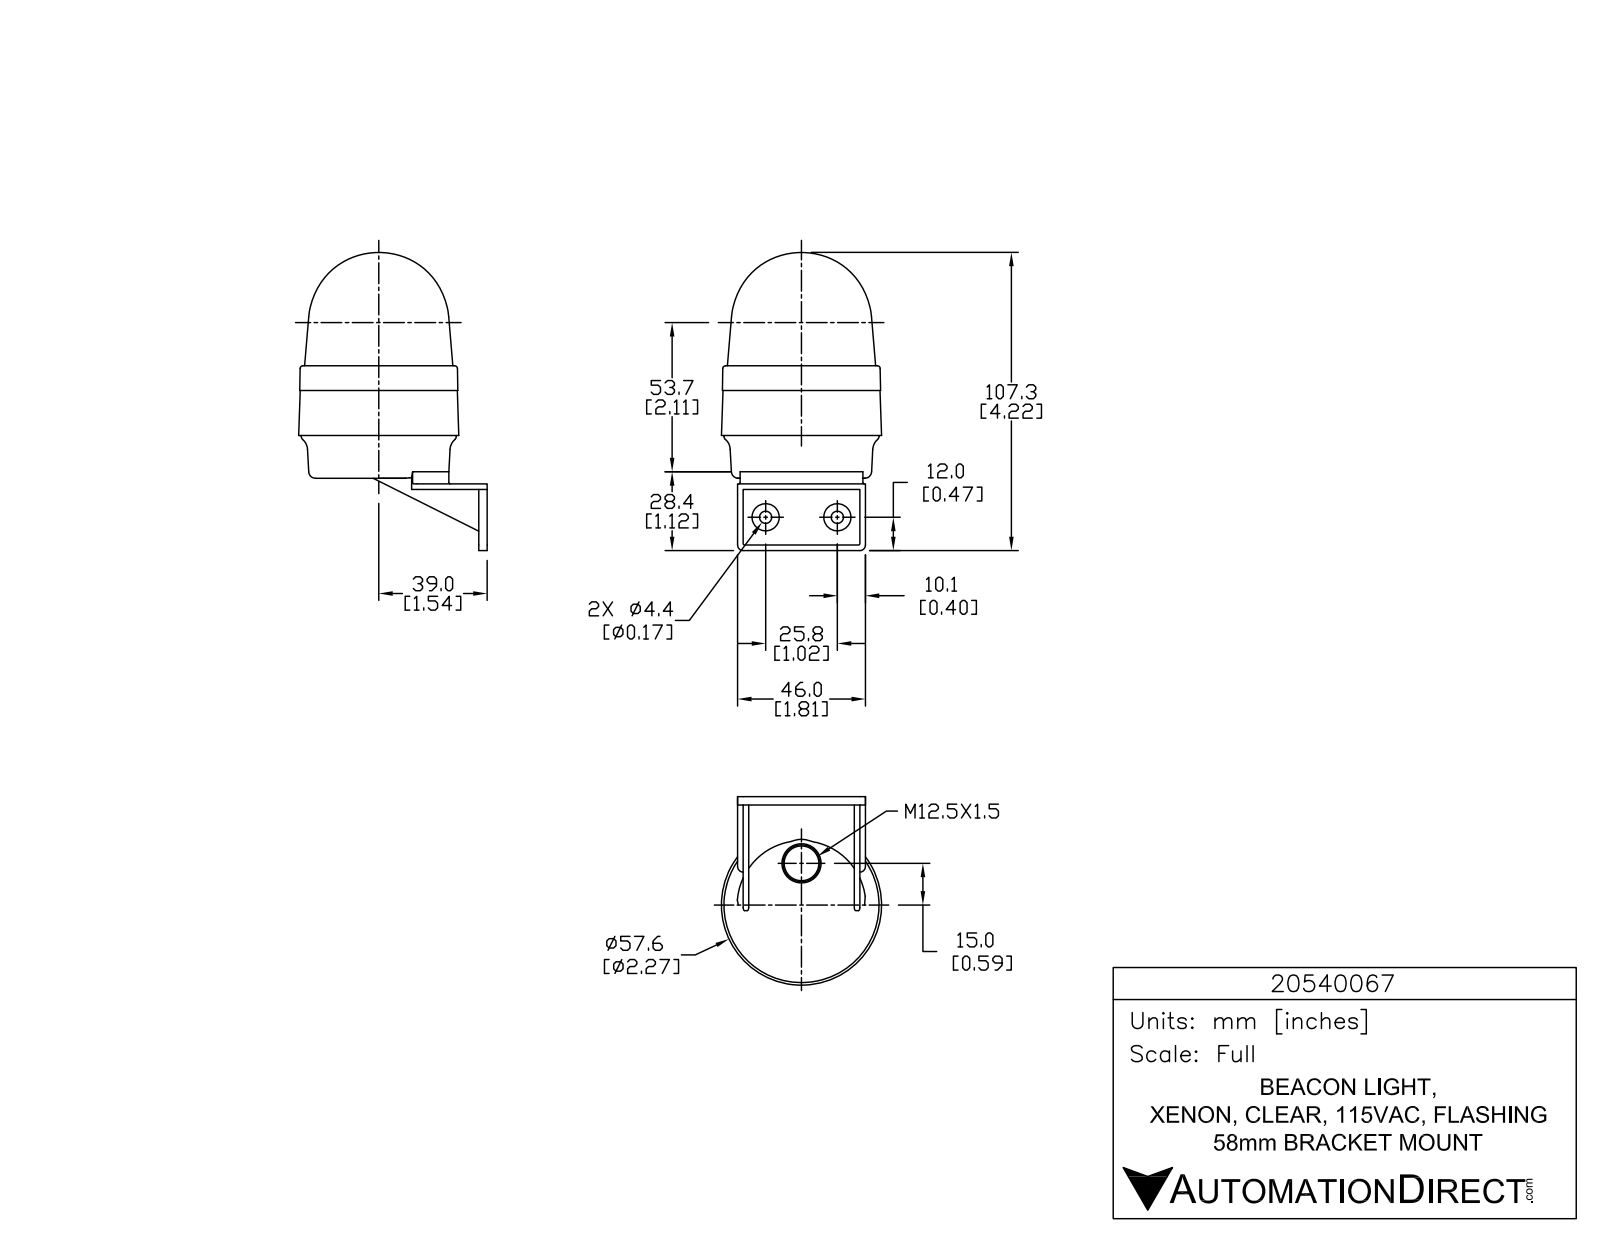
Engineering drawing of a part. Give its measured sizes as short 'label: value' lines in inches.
name: 20540067
written by: SolidWorks 2015 (AUTOMOTIVE_DESIGN)
unit: in
bodies: 1 solid, 828 faces (551 planar, 179 cylindrical, 98 other)
size: 4.225 × 2.852 × 2.407
volume: 10.27 in³; area: 33.38 in²
holes: 3× ⌀0.039, 2× ⌀0.173
bosses: 3× ⌀0.226, 3× ⌀0.056, 2× ⌀0.386, 1× ⌀2.197
rounds: 6× R0.008, 6× R0.008, 6× R0.008, 6× R0.02, 6× R0.131, 4× R0.079, 3× R0.004, 3× R0.005
face distances: 0.079, 0.157, 1.575, 1.654, 0.039, 0.118, 1.496, 0.866, 0.945, 0.764
hole spacings: 1.016
